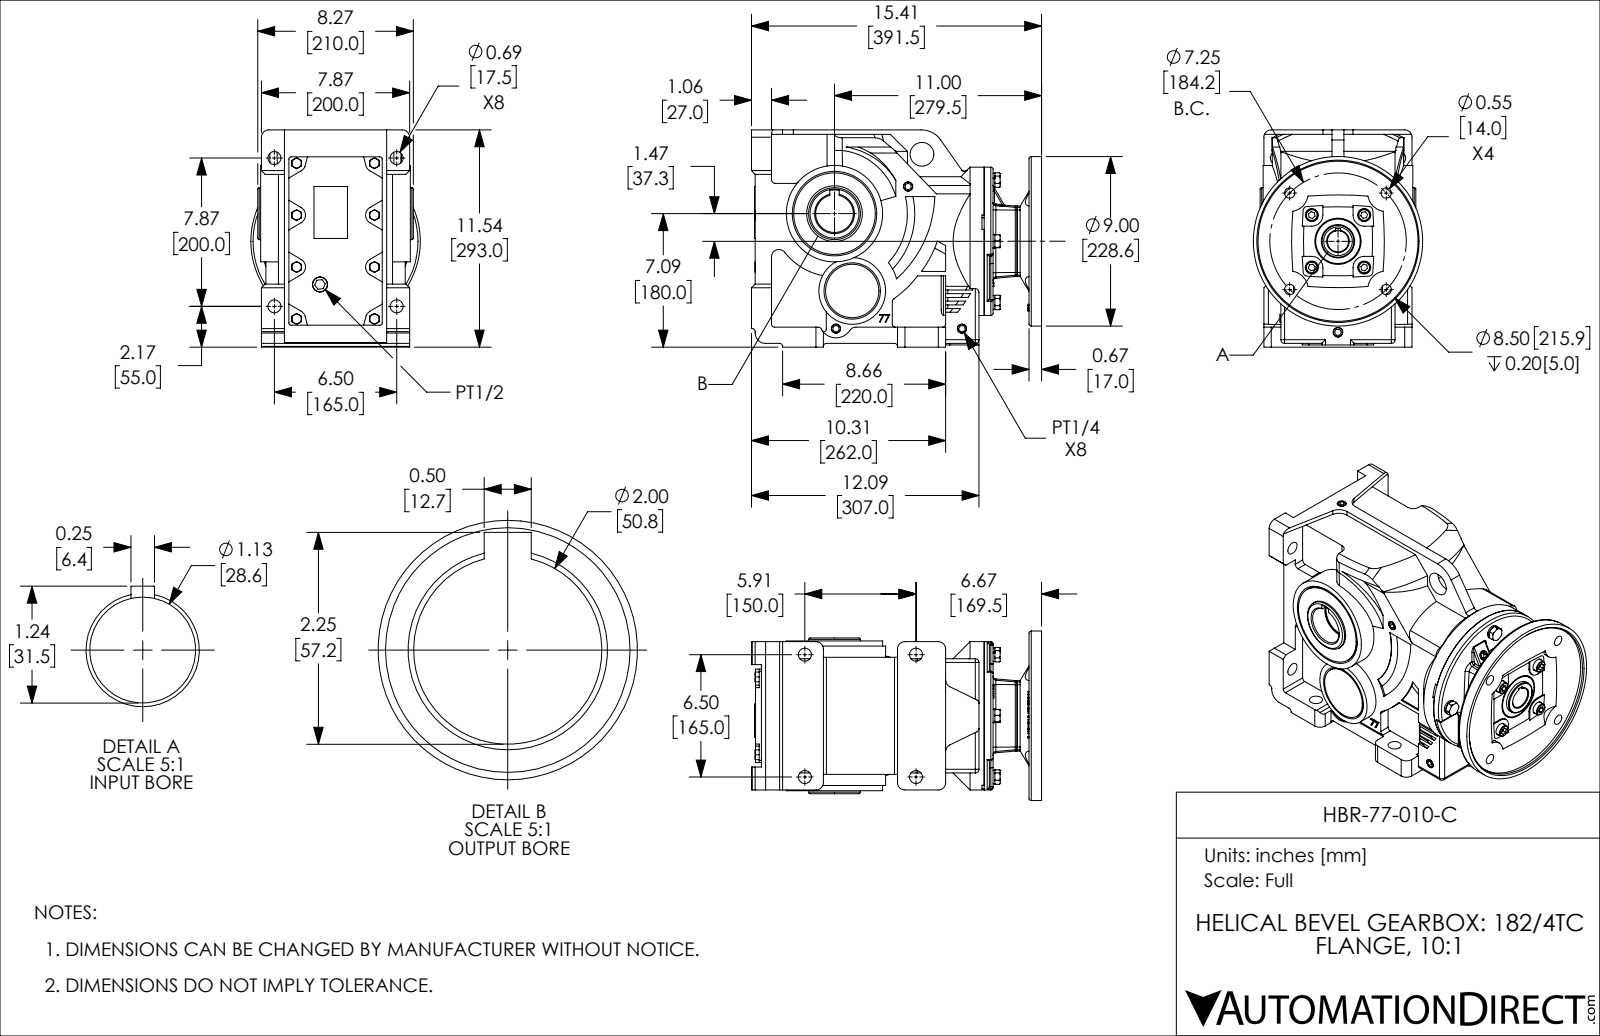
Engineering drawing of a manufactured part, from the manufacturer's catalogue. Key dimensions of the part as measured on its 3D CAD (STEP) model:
Part name (STEP PRODUCT): HBR-77-010-C
STEP written by: SolidWorks 2018 (AUTOMOTIVE_DESIGN)
Units: inches
Bodies: 43 solids, 1761 faces (783 planar, 582 cylindrical, 396 other)
Overall size (bounding box): 15.413 × 11.535 × 9
Volume: 339.1 in³ · Surface area: 1 869 in²
Round holes (diameter × count): ⌀0.689 ×12, ⌀0.268 ×8, ⌀0.335 ×8, ⌀0.354 ×8, ⌀0.433 ×8, ⌀0.394 ×4, ⌀0.402 ×4, ⌀0.551 ×4, ⌀0.438 ×3, ⌀0.118 ×2, ⌀0.487 ×2, ⌀2.165 ×2
Round bosses / shafts (diameter × count): ⌀0.315 ×8, ⌀0.63 ×5, ⌀0.724 ×4, ⌀0.394 ×4, ⌀9 ×1, ⌀7.874 ×1, ⌀5.118 ×1, ⌀3.543 ×1
Partial cylindrical surfaces — rounded edges, fillets, slot ends (radius × count): R0.394 ×36, R0.118 ×14, R0.197 ×12, R0.315 ×12, R0.157 ×11, R0.472 ×10, R0.591 ×7, R0.079 ×5
Main face-to-face distances: 0.236, 0.472, 0.315, 4.961, 0.276, 5.748, 0.787, 5.276, 0.512, 0.551
Hole centre spacings: 2.653, 2.756, 4.844, 4.968, 6.352, 6.496, 1.656, 2.32
